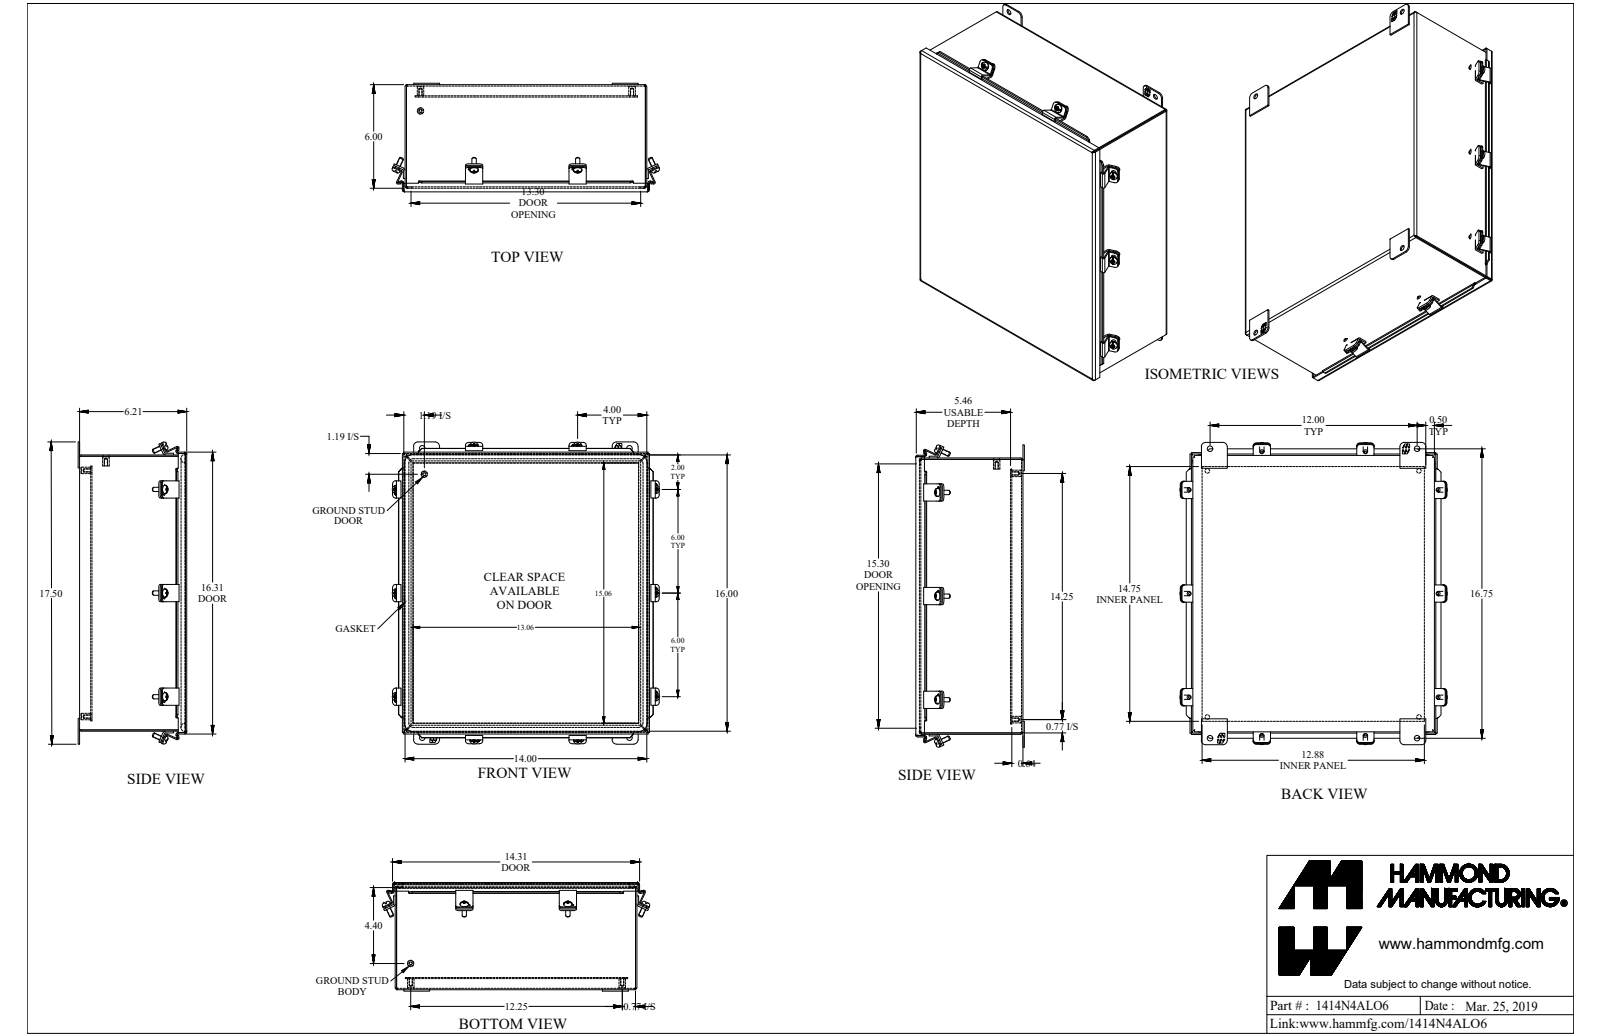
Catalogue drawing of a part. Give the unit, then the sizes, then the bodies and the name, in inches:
Units: inches
Overall size (bounding box): 17.5 × 15.49 × 6.286
Round holes (diameter × count): ⌀0.213 ×10, ⌀0.159 ×6, ⌀0.265 ×4, ⌀0.313 ×4
Round bosses / shafts (diameter × count): ⌀0.48 ×10, ⌀0.25 ×10, ⌀0.375 ×6, ⌀0.33 ×6
Partial cylindrical surfaces — rounded edges, fillets, slot ends (radius × count): R0.141 ×20, R0.188 ×20, R0.25 ×12, R0.01 ×8, R0.029 ×8, R0.036 ×8, R0.048 ×8, R0.086 ×8
Main face-to-face distances: 0.081, 6.125, 6.206, 6.044, 0.562, 0.643, 5.563, 5.482, 5.491, 5.41
Hole centre spacings: 6, 12, 12.25, 14.25, 16.75, 18.792, 20.605, 0.31
Volume: 92.4 in³ · Surface area: 2 347 in²
Bodies: 44 solids, 1213 faces (829 planar, 276 cylindrical, 108 other)
Part name (STEP PRODUCT): 1414N4ALO6
STEP written by: SolidWorks 2018 (AUTOMOTIVE_DESIGN)
